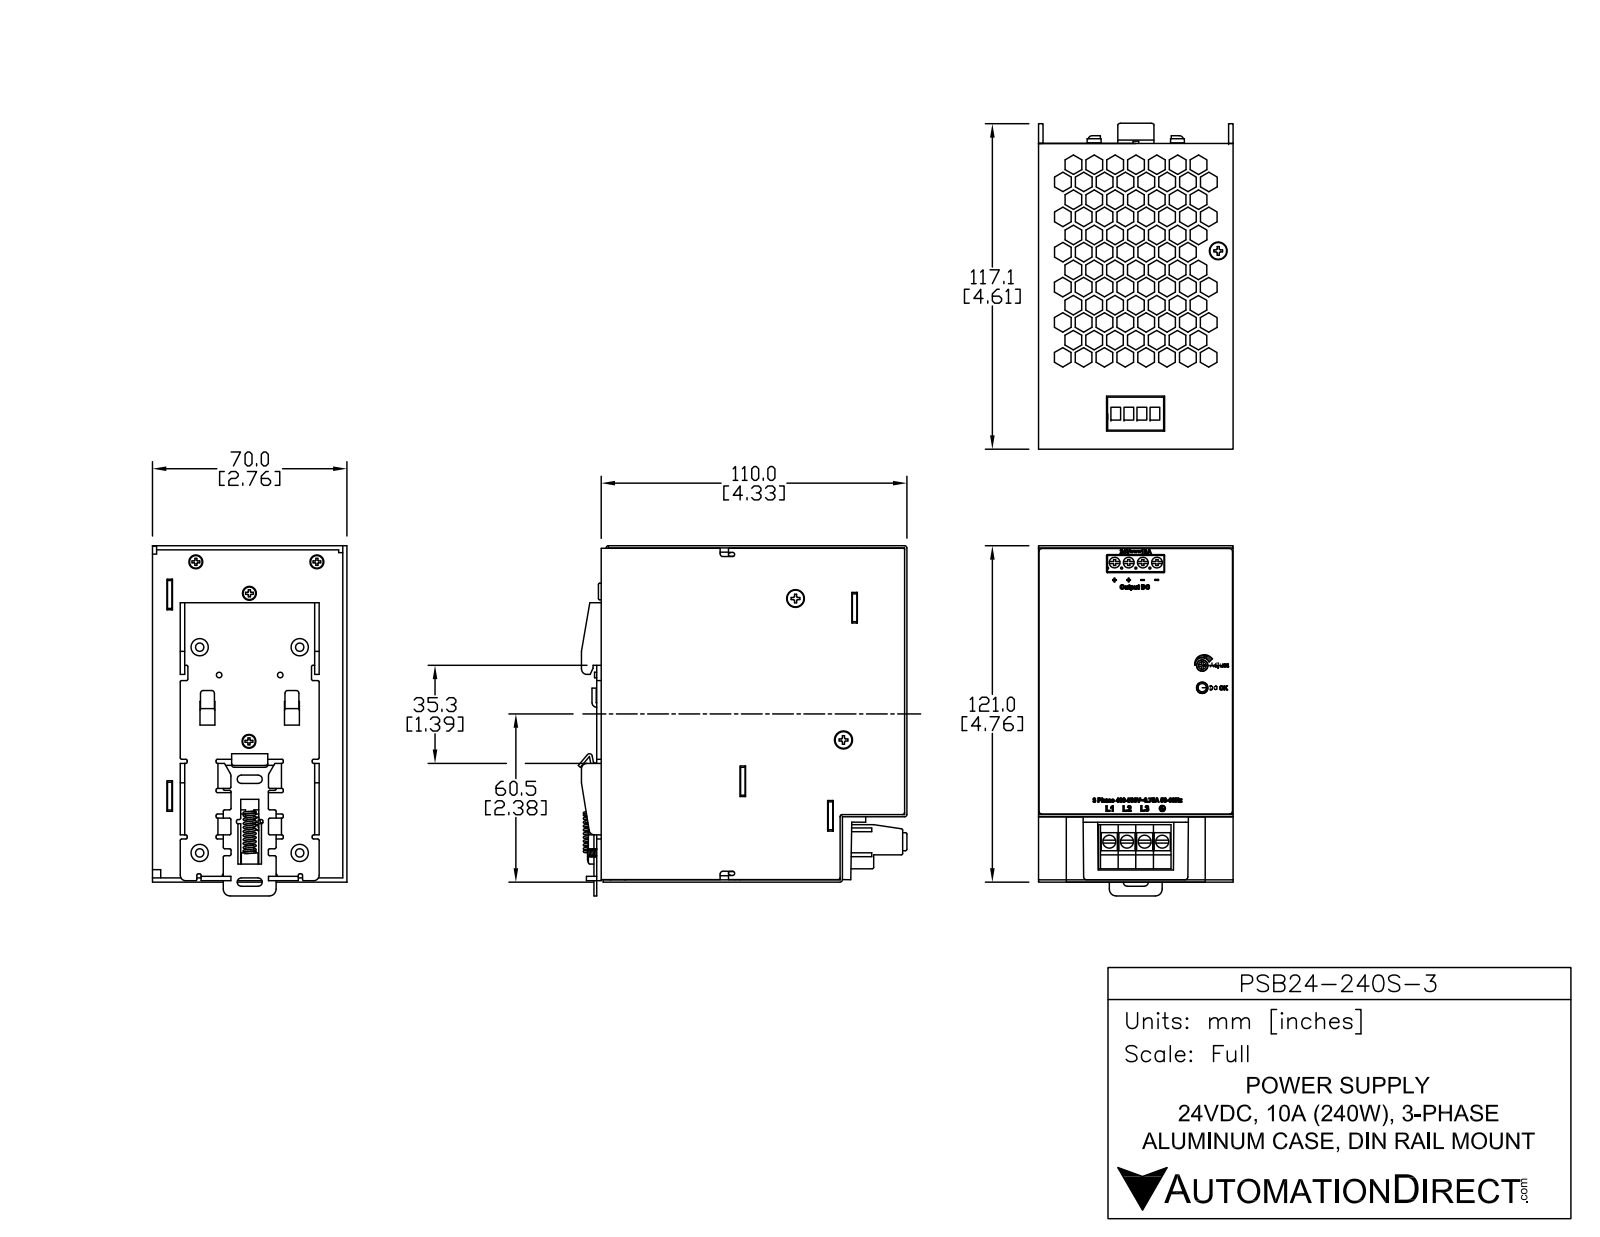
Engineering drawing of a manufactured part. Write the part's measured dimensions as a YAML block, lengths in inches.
part_name: "ASSY_DCT-1519_ASM; 334706930000; 330315490000; ASSY_PWB_DRP024V240W3BD_ASM (+8 more)"
step_written_by: "SolidWorks 2014 (AUTOMOTIVE_DESIGN)"
units: inches
bodies: {solids: 65, faces: 7532, planar: 5033, cylindrical: 1062, other: 1437}
overall_size: [4.961, 4.665, 2.759]
volume: 9.591
surface_area: 366.5
round_holes:
  - {diameter: 0.098, count: 21}
  - {diameter: 0.165, count: 9}
  - {diameter: 0.079, count: 6}
  - {diameter: 0.126, count: 5}
  - {diameter: 0.138, count: 5}
  - {diameter: 0.063, count: 4}
  - {diameter: 0.071, count: 4}
  - {diameter: 0.11, count: 4}
  - {diameter: 0.152, count: 4}
  - {diameter: 0.157, count: 4}
  - {diameter: 0.159, count: 4}
  - {diameter: 0.183, count: 4}
round_bosses_or_shafts:
  - {diameter: 0.118, count: 17}
  - {diameter: 0.236, count: 13}
  - {diameter: 0.138, count: 8}
  - {diameter: 0.226, count: 4}
  - {diameter: 0.187, count: 4}
  - {diameter: 0.177, count: 4}
  - {diameter: 0.157, count: 4}
  - {diameter: 0.156, count: 4}
partial_cylinders:
  - {radius: 0.02, count: 111}
  - {radius: 0.039, count: 60}
  - {radius: 0.03, count: 50}
  - {radius: 0.006, count: 32}
  - {radius: 0.004, count: 21}
  - {radius: 0.008, count: 20}
  - {radius: 0.035, count: 16}
  - {radius: 0.031, count: 15}
face_to_face_distances: [0.059, 0.063, 2.697, 0.031, 2.417, 2.756, 2.638, 0.28, 0.22, 2.476]
hole_center_spacings: [0.24, 1.969, 0.197, 0.295, 0.355, 0.481, 0.492, 0.66]
